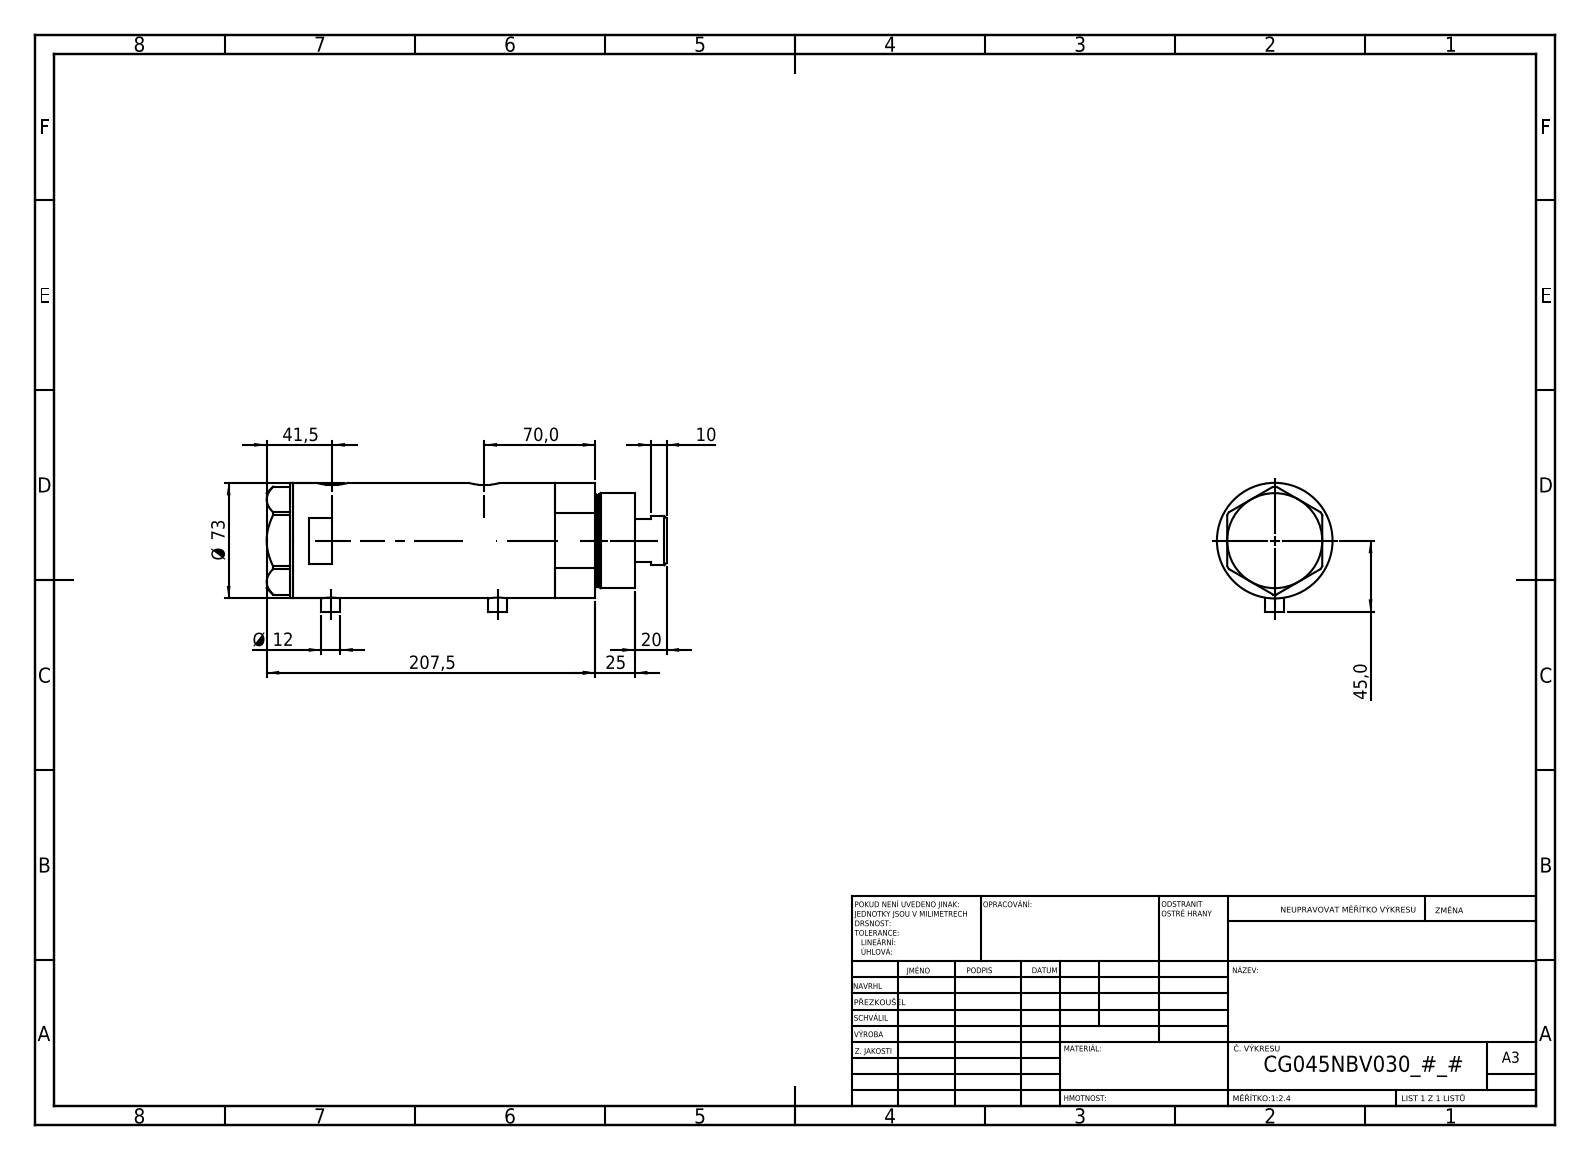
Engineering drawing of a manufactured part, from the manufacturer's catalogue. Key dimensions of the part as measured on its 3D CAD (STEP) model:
Part name (STEP PRODUCT): V270CG_BACK; V270CG_FRONT; V270CG_VC; V270CG_MIDDLE
STEP written by: SolidWorks 2019 (CONFIG_CONTROL_DESIGN)
Units: millimetres
Bodies: 4 solids, 120 faces (49 planar, 51 cylindrical, 20 other)
Overall size (bounding box): 252.5 × 81.5 × 73
Volume: 901 868 mm³ · Surface area: 149 768 mm²
Round holes (diameter × count): ⌀12.5 ×2, ⌀13.16 ×2, ⌀10.5 ×1, ⌀32 ×1, ⌀33.5 ×1, ⌀45 ×1, ⌀48 ×1, ⌀64 ×1
Round bosses / shafts (diameter × count): ⌀12 ×2, ⌀73 ×1, ⌀60 ×1, ⌀58 ×1, ⌀31 ×1
Partial cylindrical surfaces — rounded edges, fillets, slot ends (radius × count): R10 ×2
Main face-to-face distances: 95, 121, 26, 16.5, 42.5, 137.5, 2, 216, 232.5, 190
Hole centre spacings: 1, 8.5, 96, 97, 104.5, 105.5
